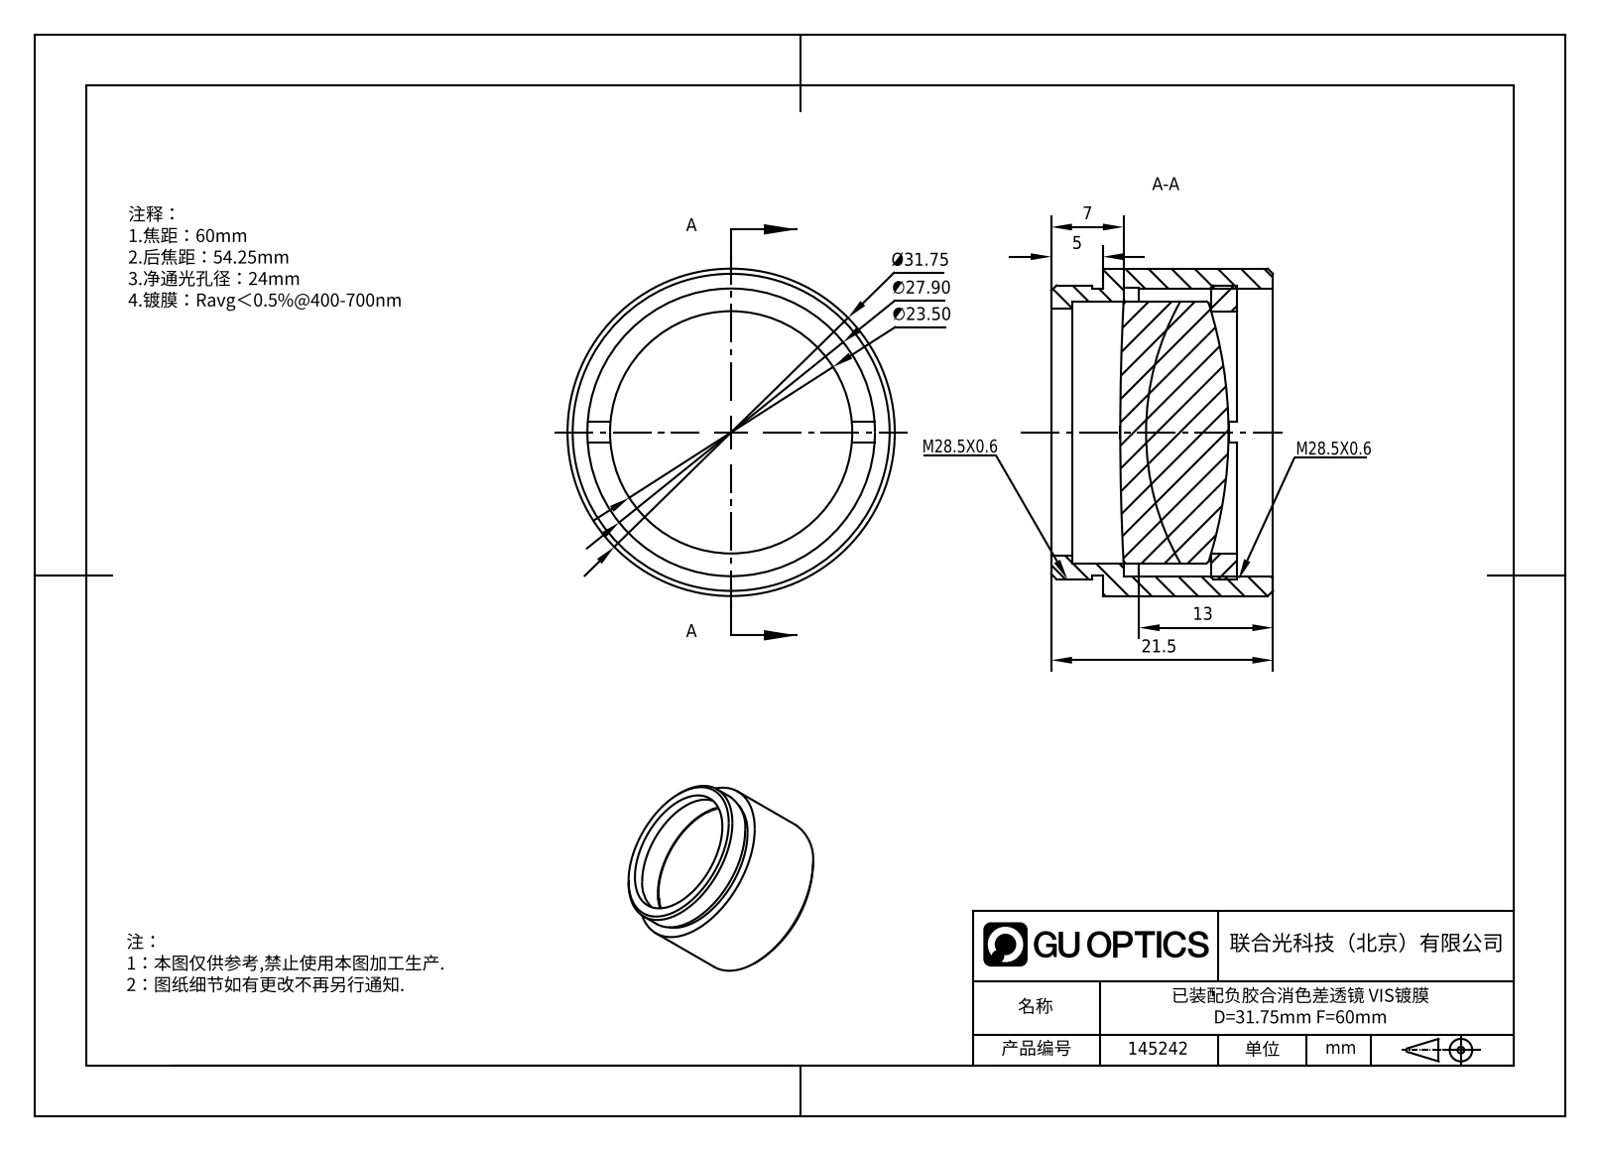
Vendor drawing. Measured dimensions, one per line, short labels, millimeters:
name: APD-ML25-060-VIS; M28.5x0.6ѹȦ; M28.5x0.6安装环PN35021-LM254-D2; GL31-025B-060-VIS_Solidworks
written by: SolidWorks 2022 (AUTOMOTIVE_DESIGN)
unit: mm
bodies: 4 solids, 56 faces (16 planar, 22 cylindrical, 18 other)
size: 31.76 × 31.76 × 21.5
volume: 9 137 mm³; area: 8 165 mm²
holes: 1× ⌀23.5, 1× ⌀24, 1× ⌀27.9, 1× ⌀28
bosses: 1× ⌀31.76, 1× ⌀28.5, 1× ⌀27.8, 1× ⌀25.4
face distances: 2, 5, 13, 2.5, 10.5, 15.5, 18, 3.5, 21.5, 16.5
